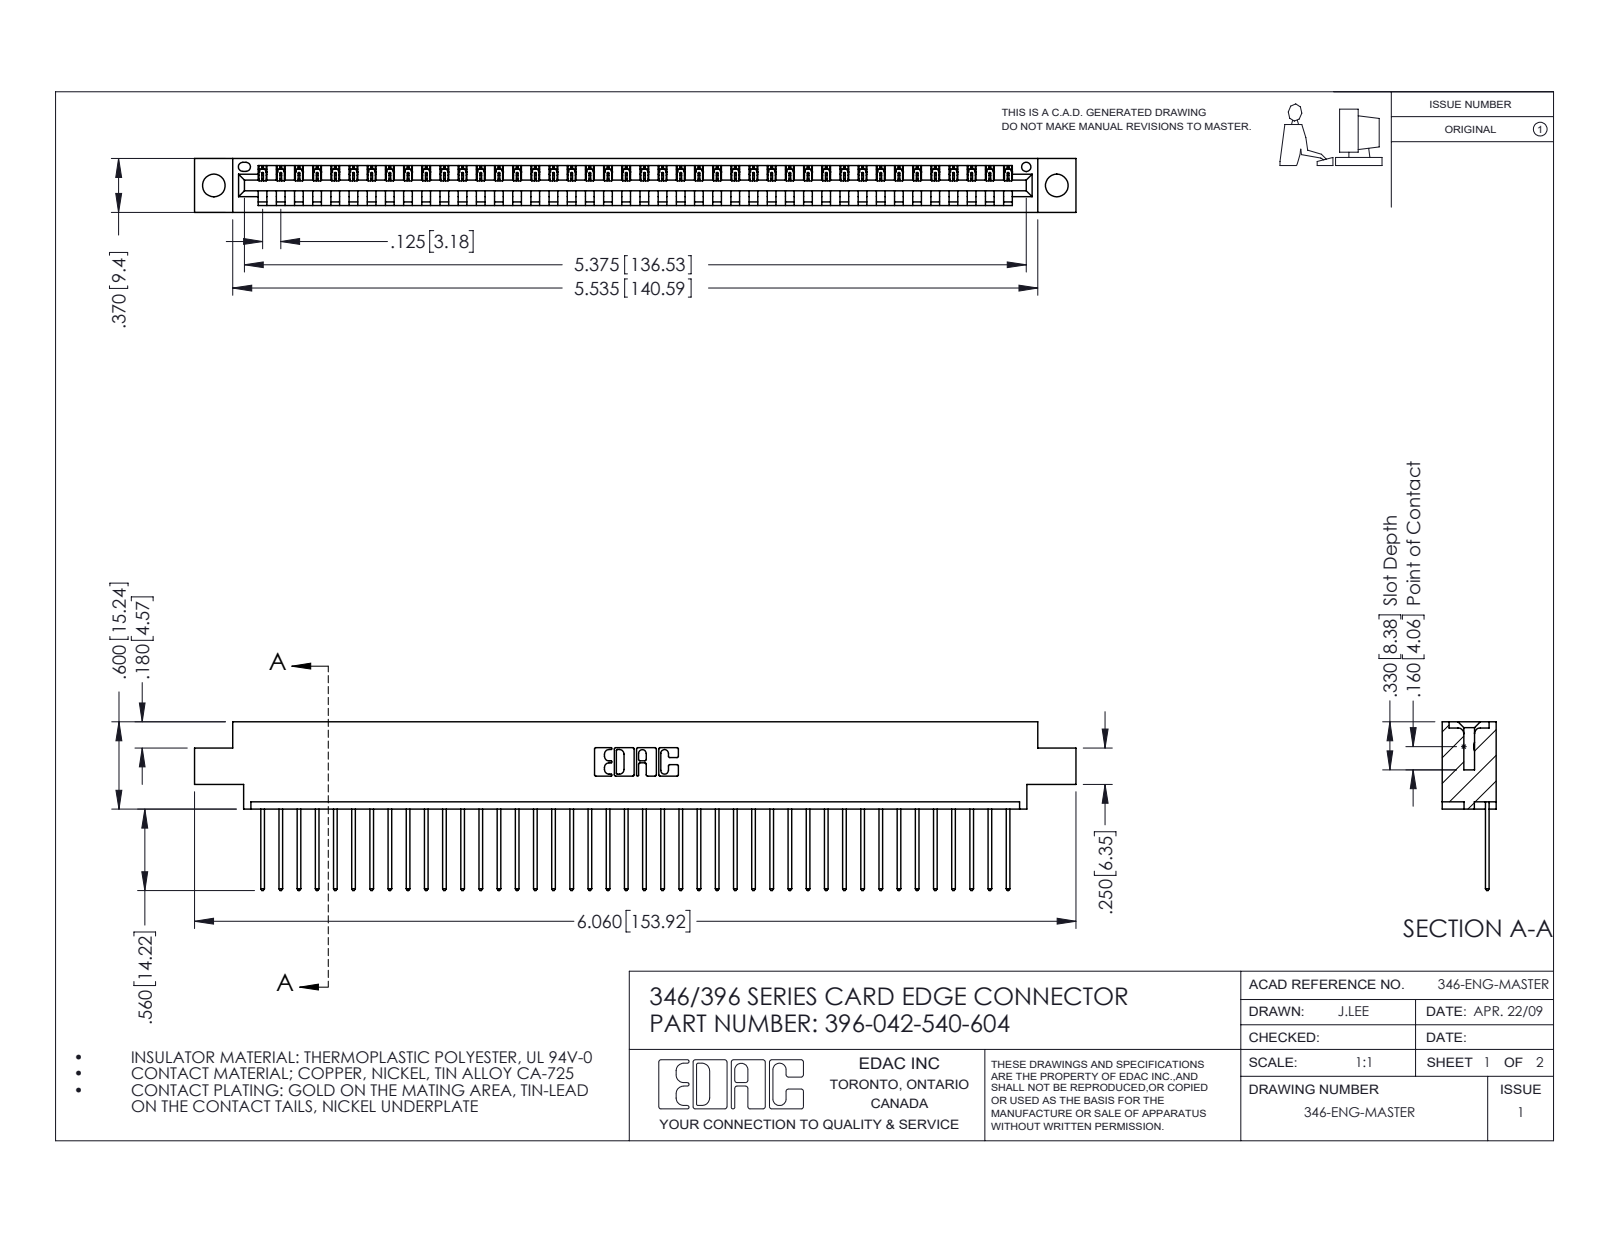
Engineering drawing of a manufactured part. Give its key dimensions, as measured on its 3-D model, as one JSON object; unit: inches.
{"part_name": "396-042-540-604; 346 Part_0.170 Offset - 0.156 Dia-TH; 345-292-001_345-293-140", "step_written_by": "SolidWorks 2016 (CONFIG_CONTROL_DESIGN)", "units": "inches", "bodies": {"solids": 43, "faces": 2562, "planar": 1760, "cylindrical": 802, "other": 0}, "overall_size": [6.06, 1.16, 0.37], "volume_in3": 0.888, "surface_area_in2": 28.77, "round_holes": [[0.156, 2], [0.064, 1]], "partial_cylinders_radius": [[0.006, 84], [0.01, 84], [0.01, 22], [0.007, 6], [0.031, 6], [0.026, 3], [0.031, 2], [0.04, 2]], "face_to_face_distances": [0.048, 0.322, 0.37, 0.25, 0.072, 0.298, 0.025, 0.148, 0.222, 0.1], "hole_center_spacings": [0.246, 5.586, 5.795]}
